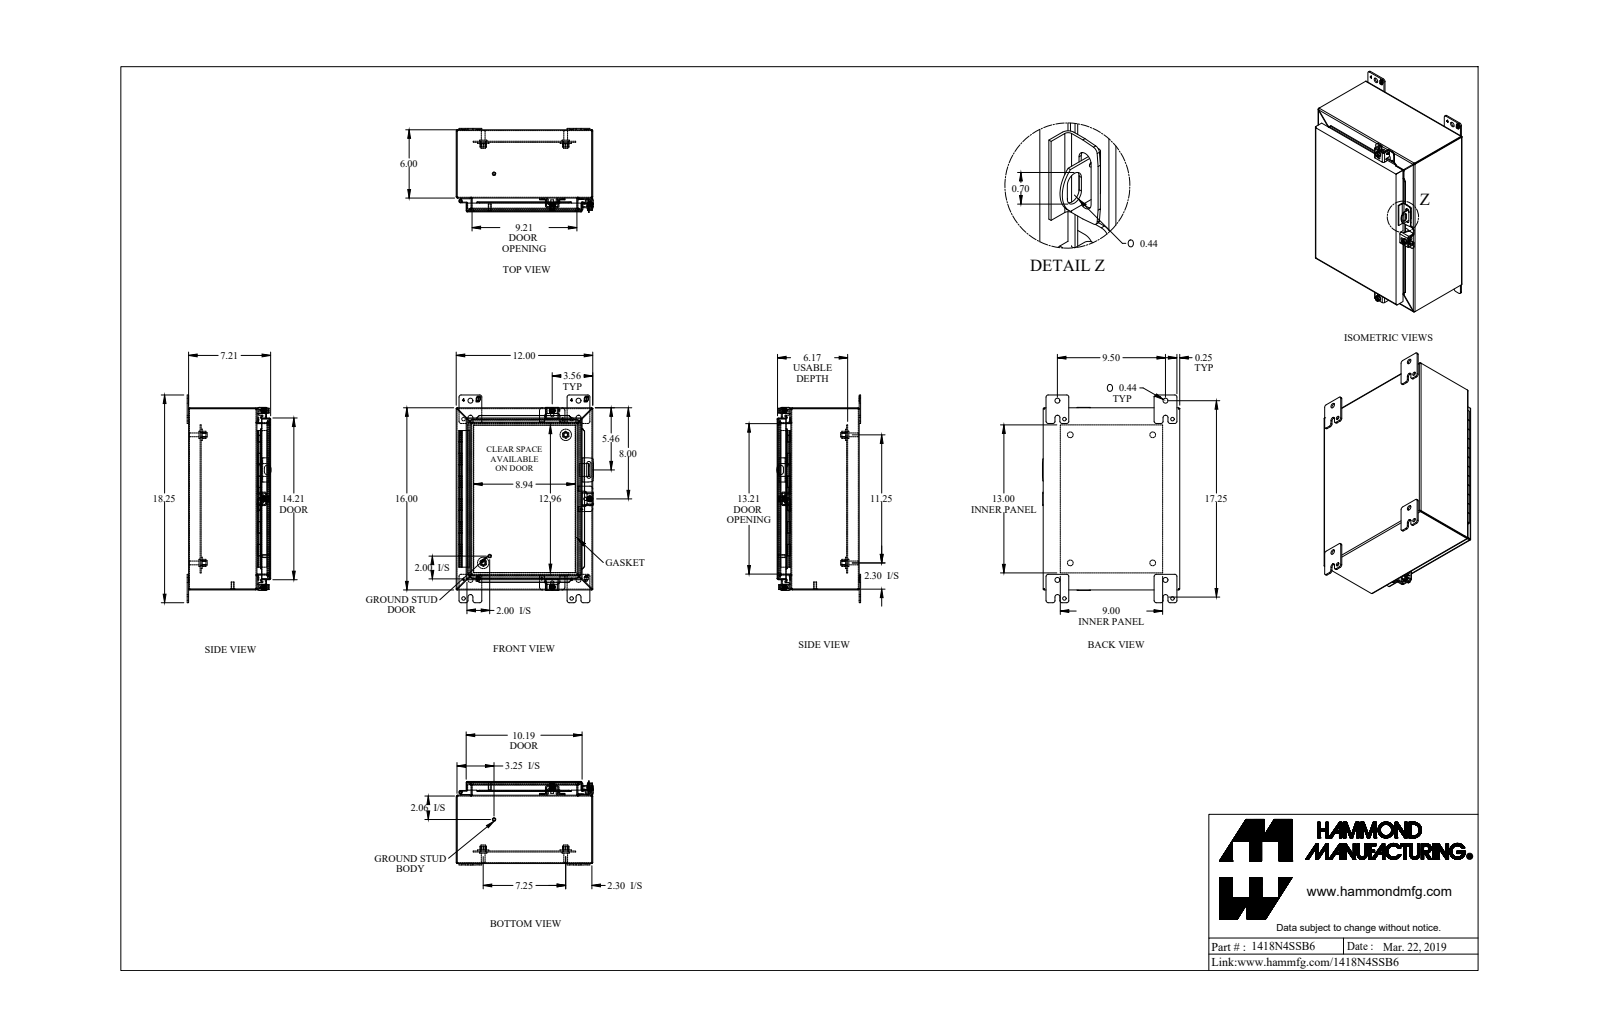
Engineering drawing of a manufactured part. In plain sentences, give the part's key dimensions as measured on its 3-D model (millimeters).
The part is named "1418N4SSB6_Default". Its 3-D file was written by "SolidWorks 2019 (CONFIG_CONTROL_DESIGN)". It is 35 solids with 1283 faces: 801 planar, 392 cylindrical and 90 other. Overall it measures 463.6 by 306.4 by 187.3 millimeters. Its volume is 1 333 000 cubic millimeters and its surface area 1 397 000 square millimeters. Round holes: 4 of diameter 8, 4 of diameter 11.1, 4 of diameter 12.7, 3 of diameter 5.4, 3 of diameter 6.7, 3 of diameter 9.5, 2 of diameter 7.8, 2 of diameter 11.3, 1 of diameter 3.2, 1 of diameter 4.7. Round bosses or shafts: 4 of diameter 16.5, 4 of diameter 9.5, 4 of diameter 8.4, 3 of diameter 12.7, 3 of diameter 9.9, 3 of diameter 6.2, 2 of diameter 25.4, 2 of diameter 8. Partial cylindrical surfaces (rounded edges, fillets, slot ends): 26 of radius 4.8, 24 of radius 0.9, 24 of radius 2.7, 16 of radius 6.4, 15 of radius 1.2, 15 of radius 3.6, 8 of radius 1.1, 8 of radius 3.2. The main face-to-face distances are 1.8, 303, 179.5, 181.3, 1.8, 181.3, 183.1, 404.6, 23.8, 150.6. The hole center spacings are 44.1, 241.3, 400.1, 467.2, 61.8, 184.2, 216.1, 285.8.
